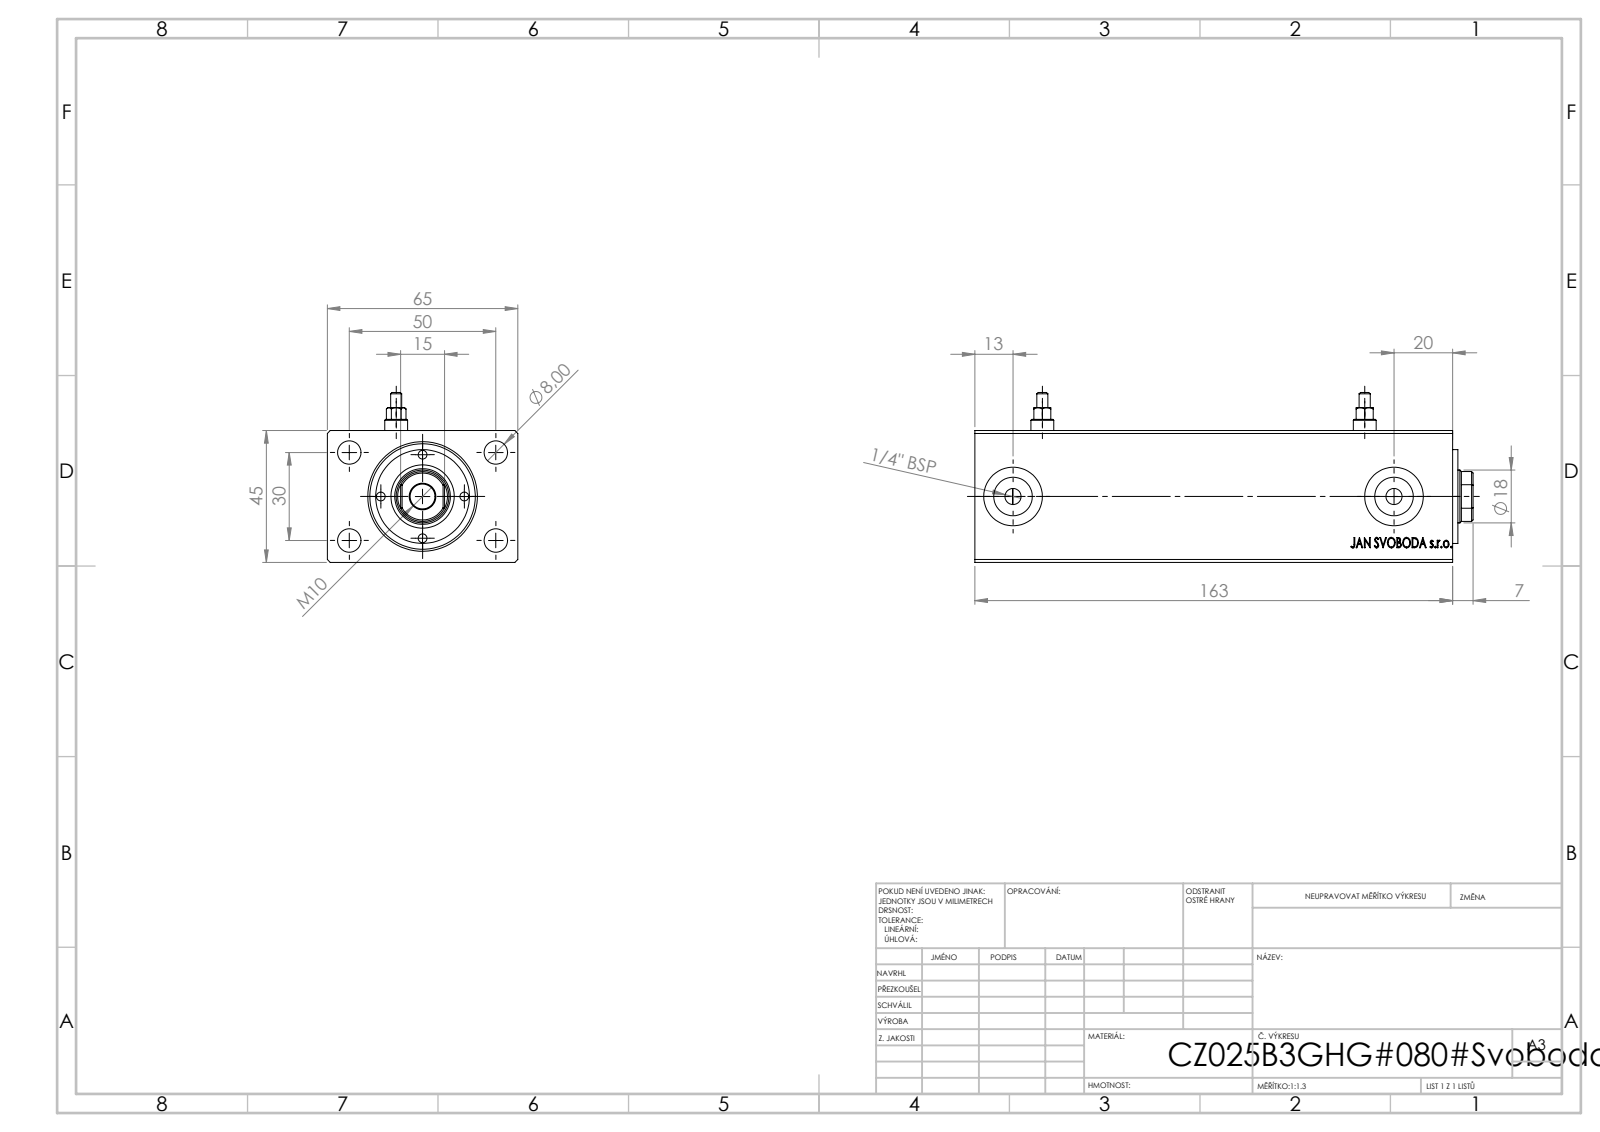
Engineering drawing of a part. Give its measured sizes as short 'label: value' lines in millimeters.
name: V500CZ; V500CZ_B_VC; Zatka_Cushioning3
written by: SolidWorks 2019 (CONFIG_CONTROL_DESIGN)
unit: mm
bodies: 5 solids, 933 faces (423 planar, 74 cylindrical, 436 other)
size: 170 × 65 × 58
volume: 443 939 mm³; area: 74 840 mm²
holes: 6× ⌀8, 4× ⌀3, 2× ⌀1.8, 2× ⌀5.5, 2× ⌀13.16, 2× ⌀20, 1× ⌀8.5, 1× ⌀18, 1× ⌀19, 1× ⌀25, 1× ⌀36
bosses: 2× ⌀7.8, 2× ⌀3.8, 1× ⌀32
rounds: 1× R8.5
face distances: 45, 65, 163, 7, 162.8, 12.8, 150.2, 12.6, 1.8, 5.2
hole spacings: 14.25, 18.45, 20.15, 25.01, 29.15, 38.48, 42.02, 28.5
